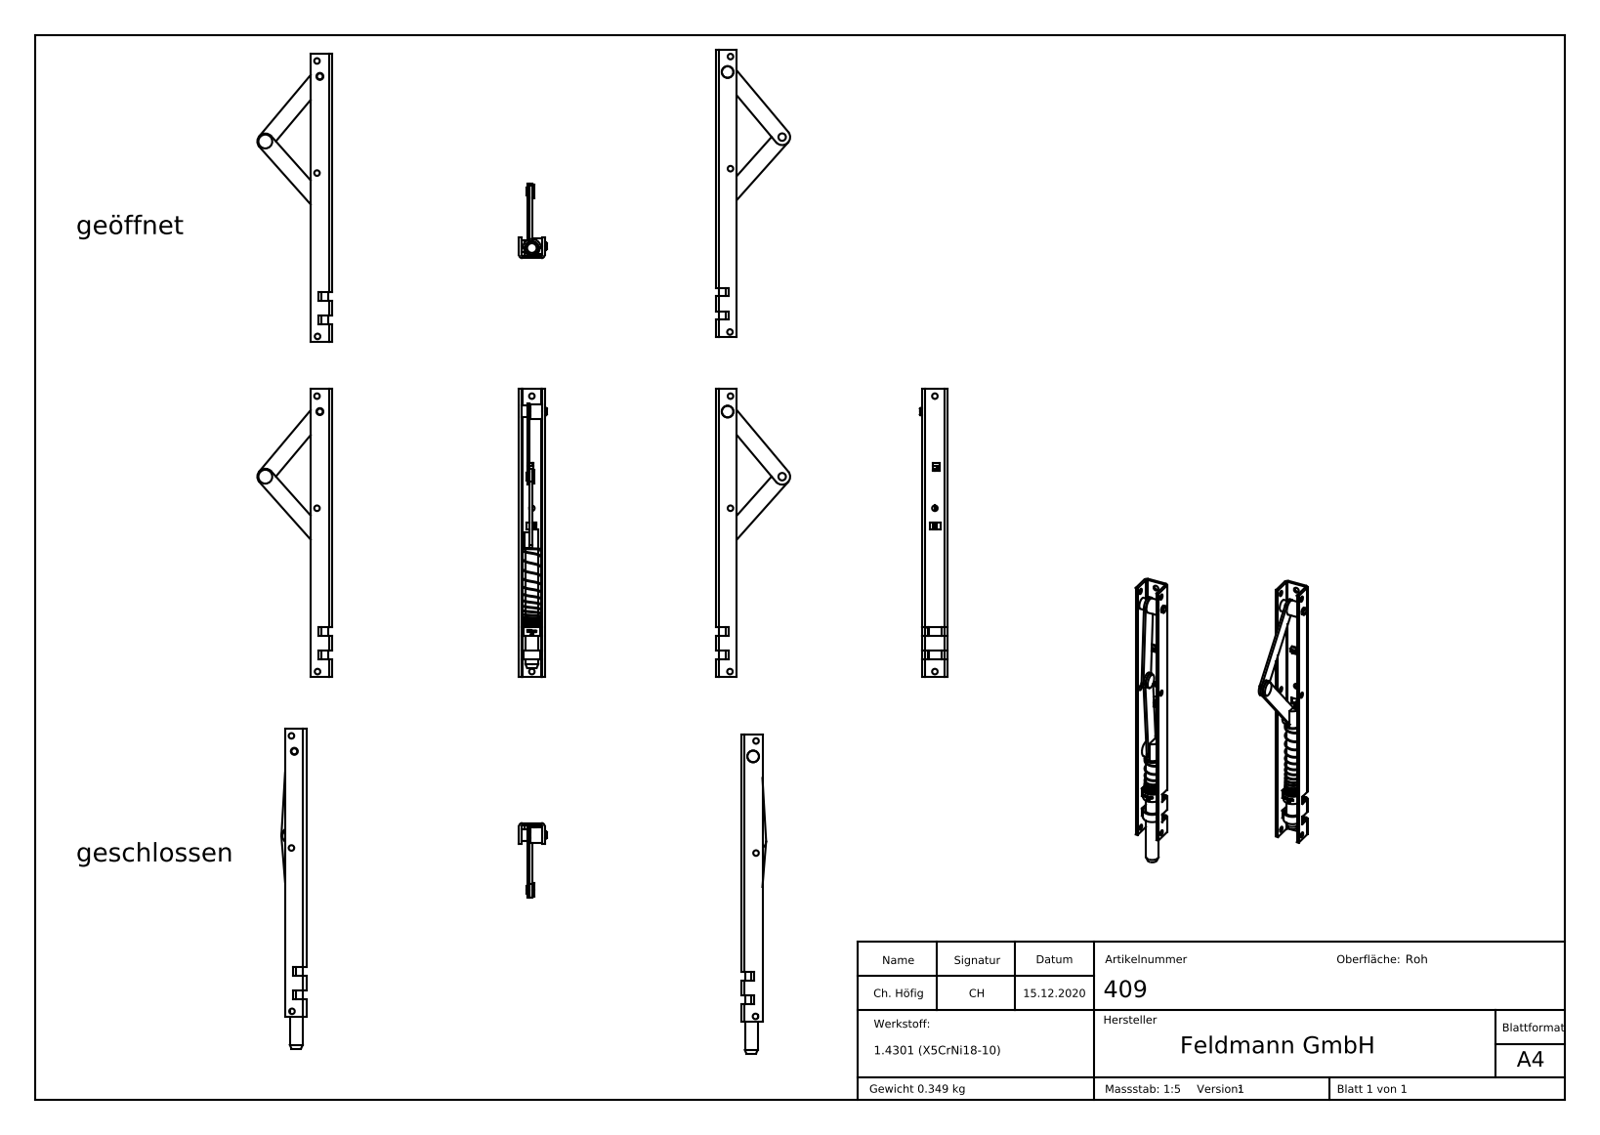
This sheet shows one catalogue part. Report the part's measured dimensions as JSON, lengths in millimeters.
{"part_name": "409 Teil4_409 Teil4; 409; 409 Teil2_409 Teil2; 409 Teil2 (+7 more)", "step_written_by": "SolidWorks 2018 (CONFIG_CONTROL_DESIGN)", "units": "millimeters", "bodies": {"solids": 8, "faces": 365, "planar": 160, "cylindrical": 113, "other": 92}, "overall_size": [270, 70, 26], "volume_mm3": 53657, "surface_area_mm2": 49264, "round_holes": [[5.2, 6], [6.5, 3], [6.2, 1], [11, 1]], "round_bosses_or_shafts": [[6, 3], [14.8, 1], [14, 1], [13, 1], [12, 1], [10.8, 1], [7, 1]], "partial_cylinders_radius": [[1, 8], [3, 6], [7.5, 3], [0.5, 2], [2.5, 2], [6.5, 1], [8.4, 1], [8.5, 1]], "face_to_face_distances": [2, 22, 10, 12, 20, 8, 14, 24, 6, 16], "hole_center_spacings": [79.7, 105.2, 153.3, 258.5, 14.75, 30.24, 56.83, 89.8]}
